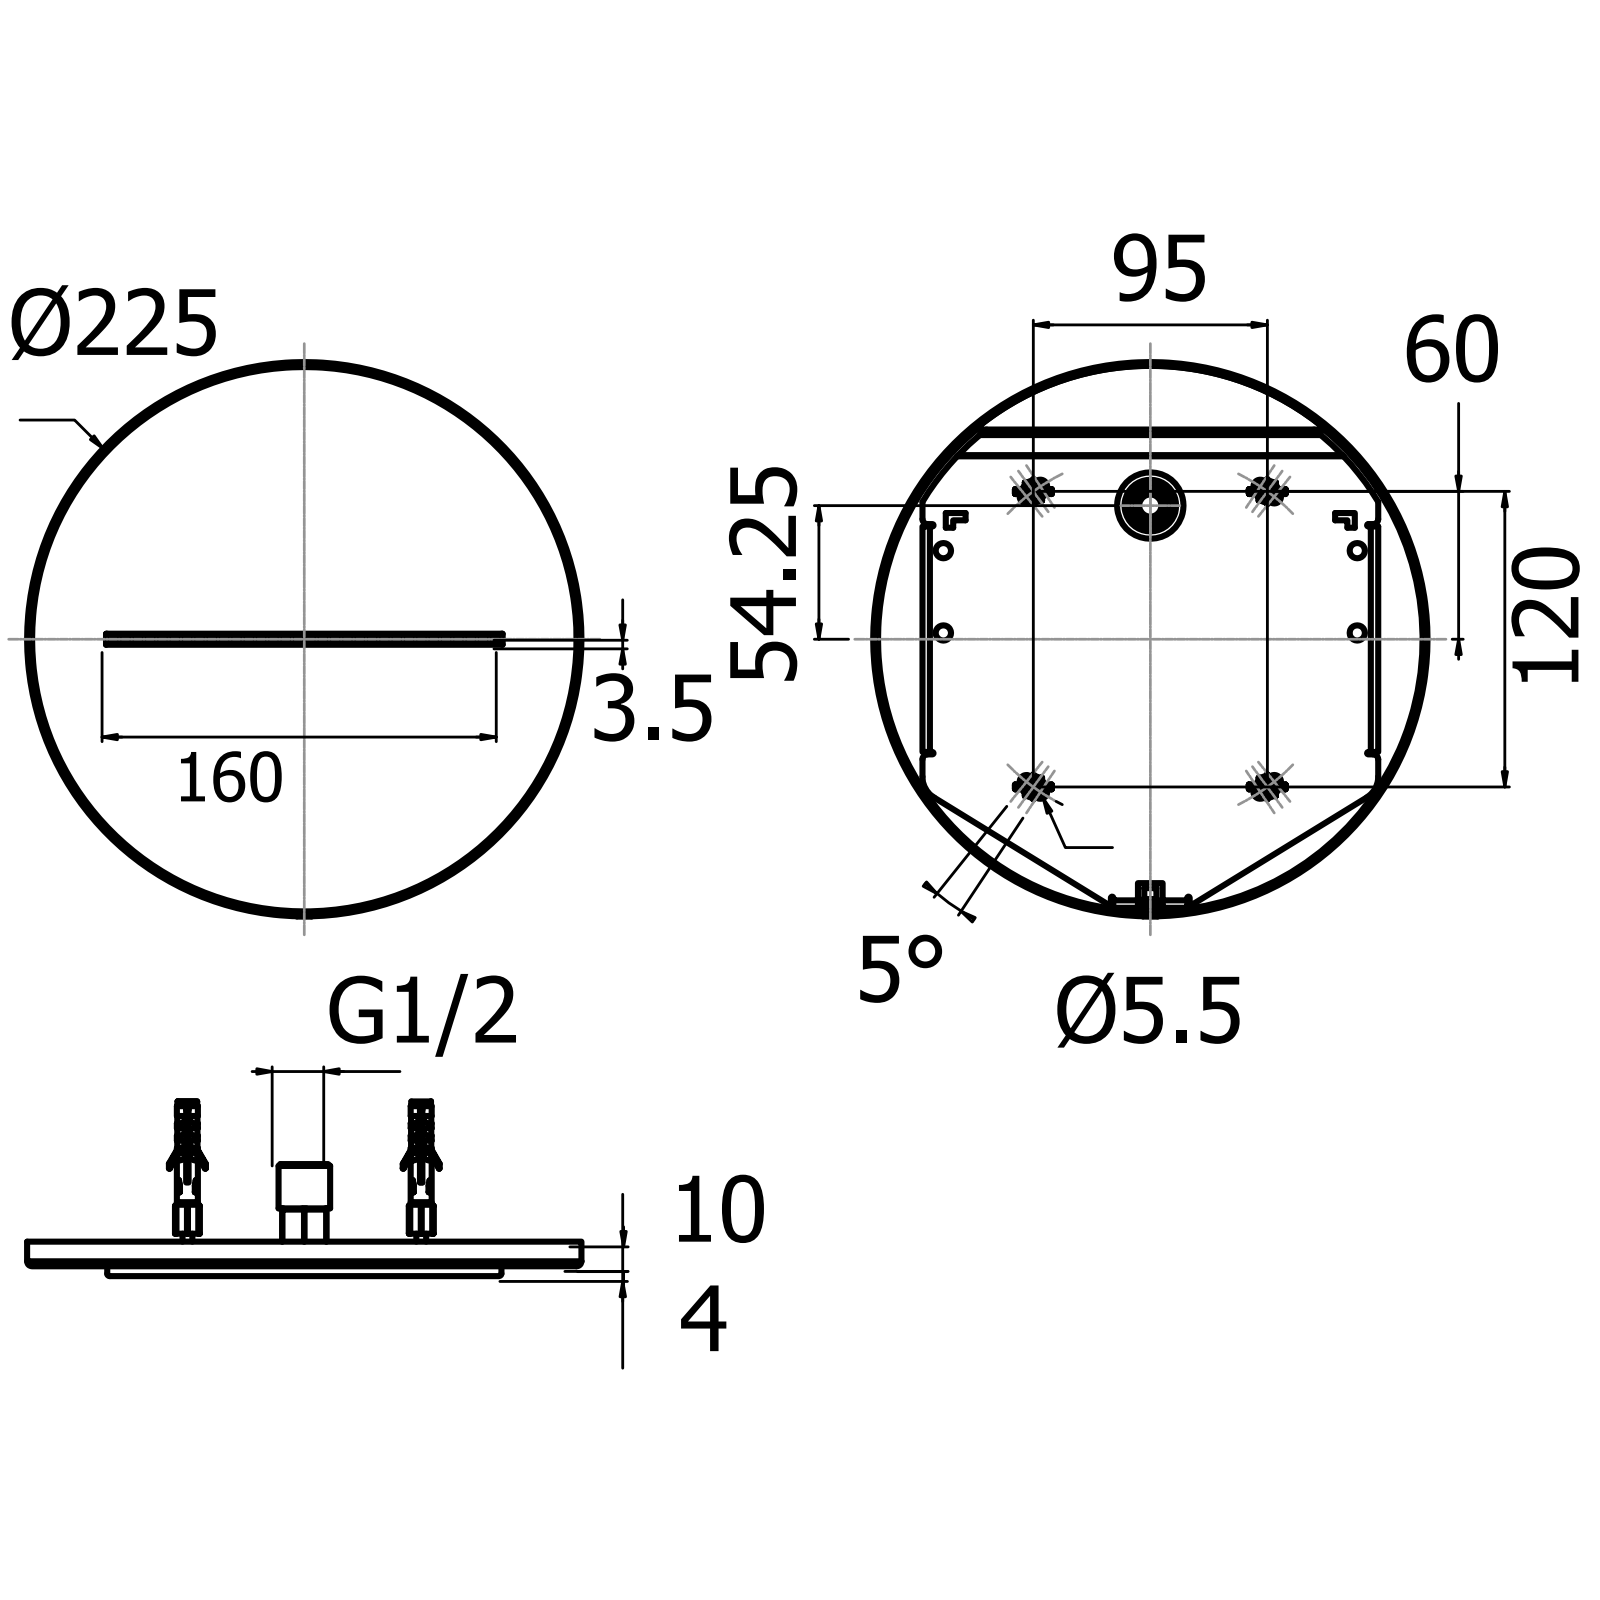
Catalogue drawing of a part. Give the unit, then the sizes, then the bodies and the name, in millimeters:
Units: millimetres
Overall size (bounding box): 225 × 225 × 39
Round holes (diameter × count): ⌀6.2 ×4, ⌀5.3 ×2, ⌀2.5 ×1, ⌀3.2 ×1, ⌀4 ×1, ⌀9 ×1, ⌀13.1 ×1, ⌀26.95 ×1, ⌀222 ×1
Round bosses / shafts (diameter × count): ⌀225 ×1, ⌀14.8 ×1, ⌀12.9 ×1, ⌀10.8 ×1, ⌀6 ×1, ⌀4.9 ×1, ⌀3 ×1, ⌀2.8 ×1
Partial cylindrical surfaces — rounded edges, fillets, slot ends (radius × count): R1 ×10, R2 ×8, R2.75 ×8, R0.5 ×6, R1.5 ×6, R3 ×5, R0.1 ×4, R10 ×4
Main face-to-face distances: 1.5, 8.5, 2.5, 1, 7, 10, 3.5, 6, 5, 4
Hole centre spacings: 16.7, 170.82, 170, 33.4, 85.04, 86.95, 87.15, 91.92
Volume: 223 719 mm³ · Surface area: 311 158 mm²
Bodies: 9 solids, 545 faces (297 planar, 209 cylindrical, 39 other)
Part name (STEP PRODUCT): A.R._24527/20220905; Art.50001
STEP written by: Spatial InterOp 3D (AUTOMOTIVE_DESIGN)
